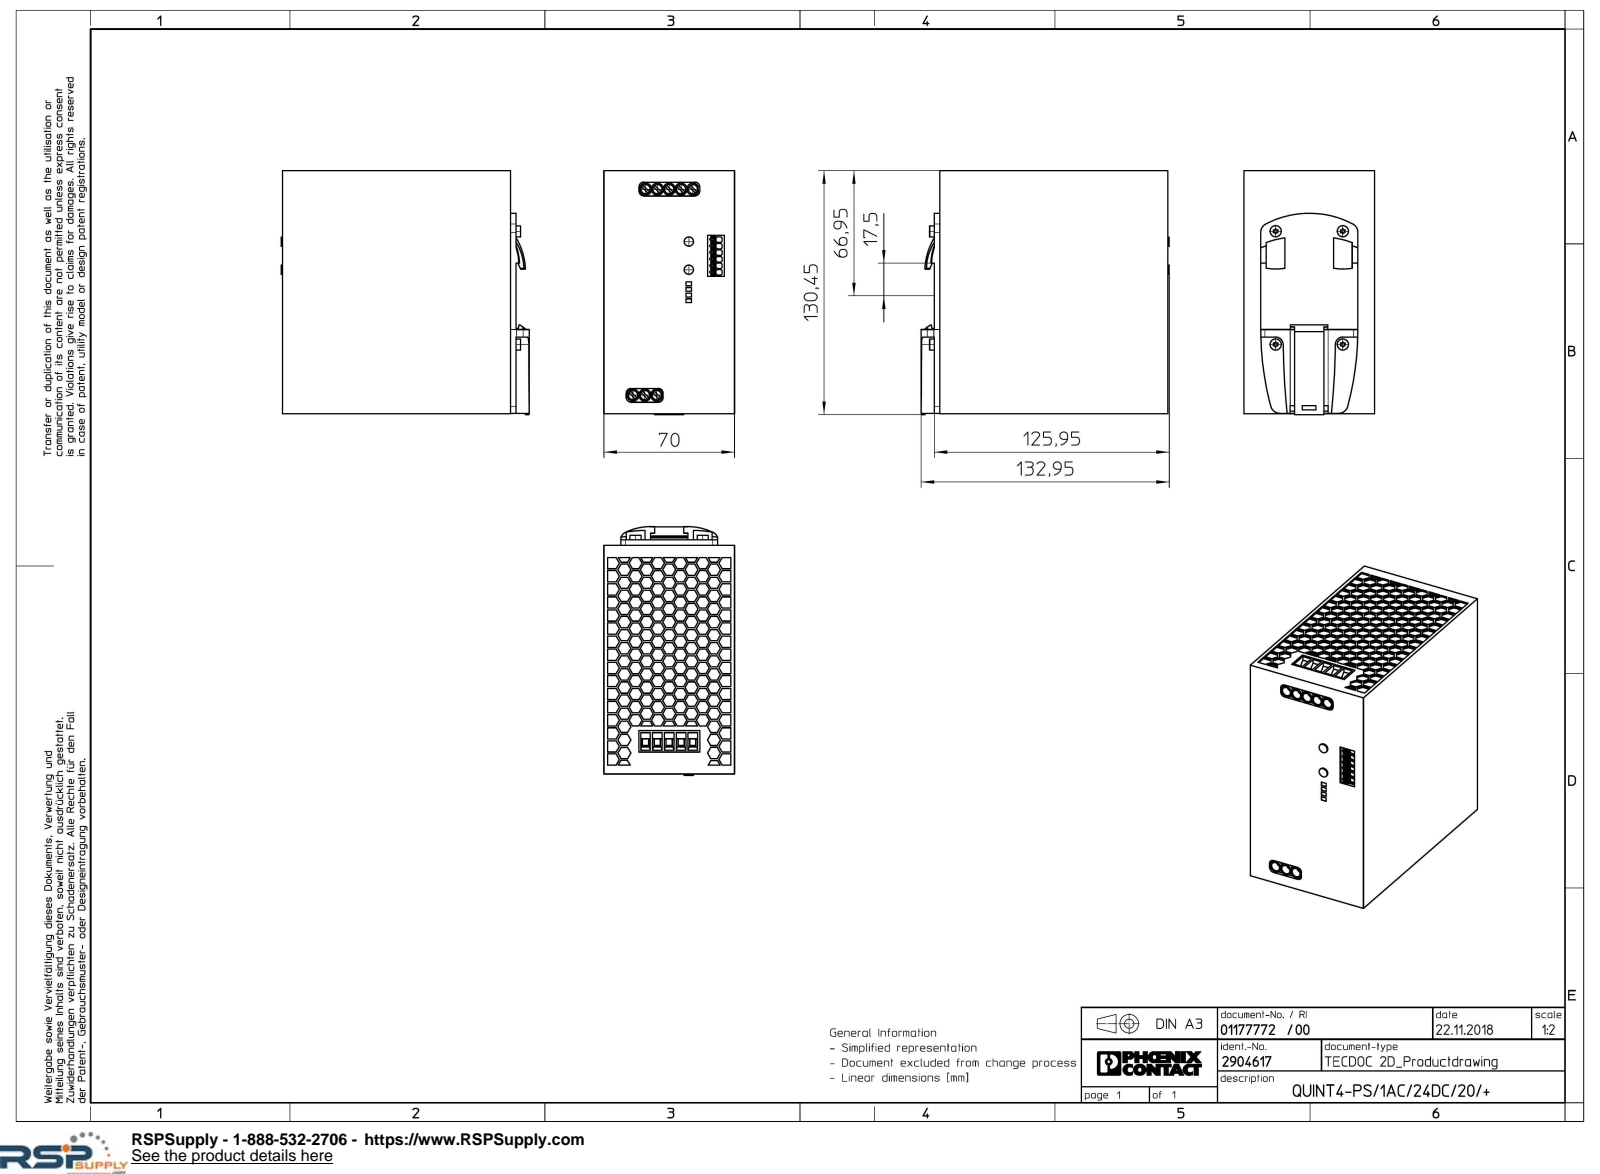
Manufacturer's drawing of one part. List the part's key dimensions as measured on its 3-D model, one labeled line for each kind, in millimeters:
Part name (STEP PRODUCT): QUINT4_PS_1AC_24DC_20_PLUS-select
STEP written by: Creo Elements/Direct Modeling 20.1A 29-Sep-2018 (C) Parametric Technology GmbH (AUTOMOTIVE_DESIGN)
Units: millimetres
Bodies: 1 solid, 2840 faces (2683 planar, 139 cylindrical, 18 other)
Overall size (bounding box): 132.95 × 130.45 × 70
Volume: 1 126 000 mm³ · Surface area: 78 921 mm²
Round holes (diameter × count): ⌀5 ×8
Round bosses / shafts (diameter × count): ⌀6 ×4, ⌀5 ×2
Partial cylindrical surfaces — rounded edges, fillets, slot ends (radius × count): R0.1 ×48, R0.97 ×12, R2.5 ×8, R3.25 ×8, R0.57 ×6, R0.6 ×6, R5 ×4, R4 ×2
Main face-to-face distances: 70, 0.8, 129.2, 128.4, 122.25, 3, 125.25, 130, 7, 6.9
Hole centre spacings: 6.35, 12.7, 19.05, 25.4
